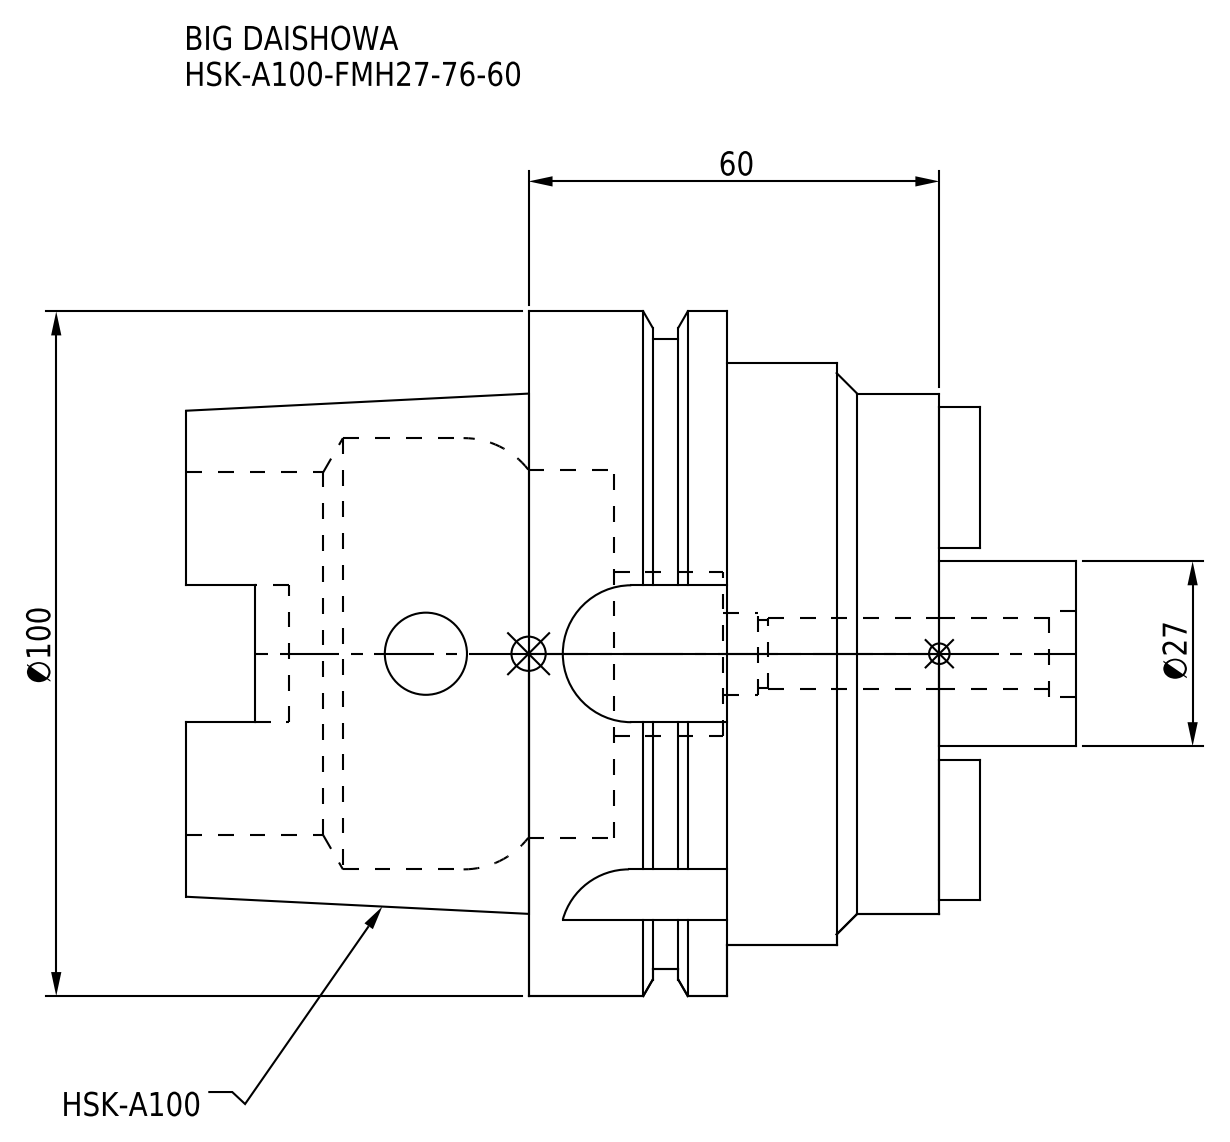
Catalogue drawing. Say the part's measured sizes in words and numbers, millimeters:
The part is named "HSK-A100-FMH27-76-60". Its 3-D file was written by "CREO PARAMETRIC BY PTC INC, 2016380 (AUTOMOTIVE_DESIGN)". It is 1 solid with 109 faces: 47 planar, 46 cylindrical and 16 other. Overall it measures 130 by 100 by 100 millimeters. Its volume is 423 243 cubic millimeters and its surface area 61 481 square millimeters. Round holes: 2 of diameter 12, 1 of diameter 10, 1 of diameter 10.3, 1 of diameter 12.5, 1 of diameter 24, 1 of diameter 53, 1 of diameter 53.8, 1 of diameter 63. Round bosses or shafts: 1 of diameter 100, 1 of diameter 92, 1 of diameter 85, 1 of diameter 76, 1 of diameter 27. Partial cylindrical surfaces (rounded edges, fillets, slot ends): 4 of radius 4.88, 4 of radius 10. The main face-to-face distances are 60, 16.55, 31, 29, 47.55, 12.45, 50, 110, 79, 62.45.
